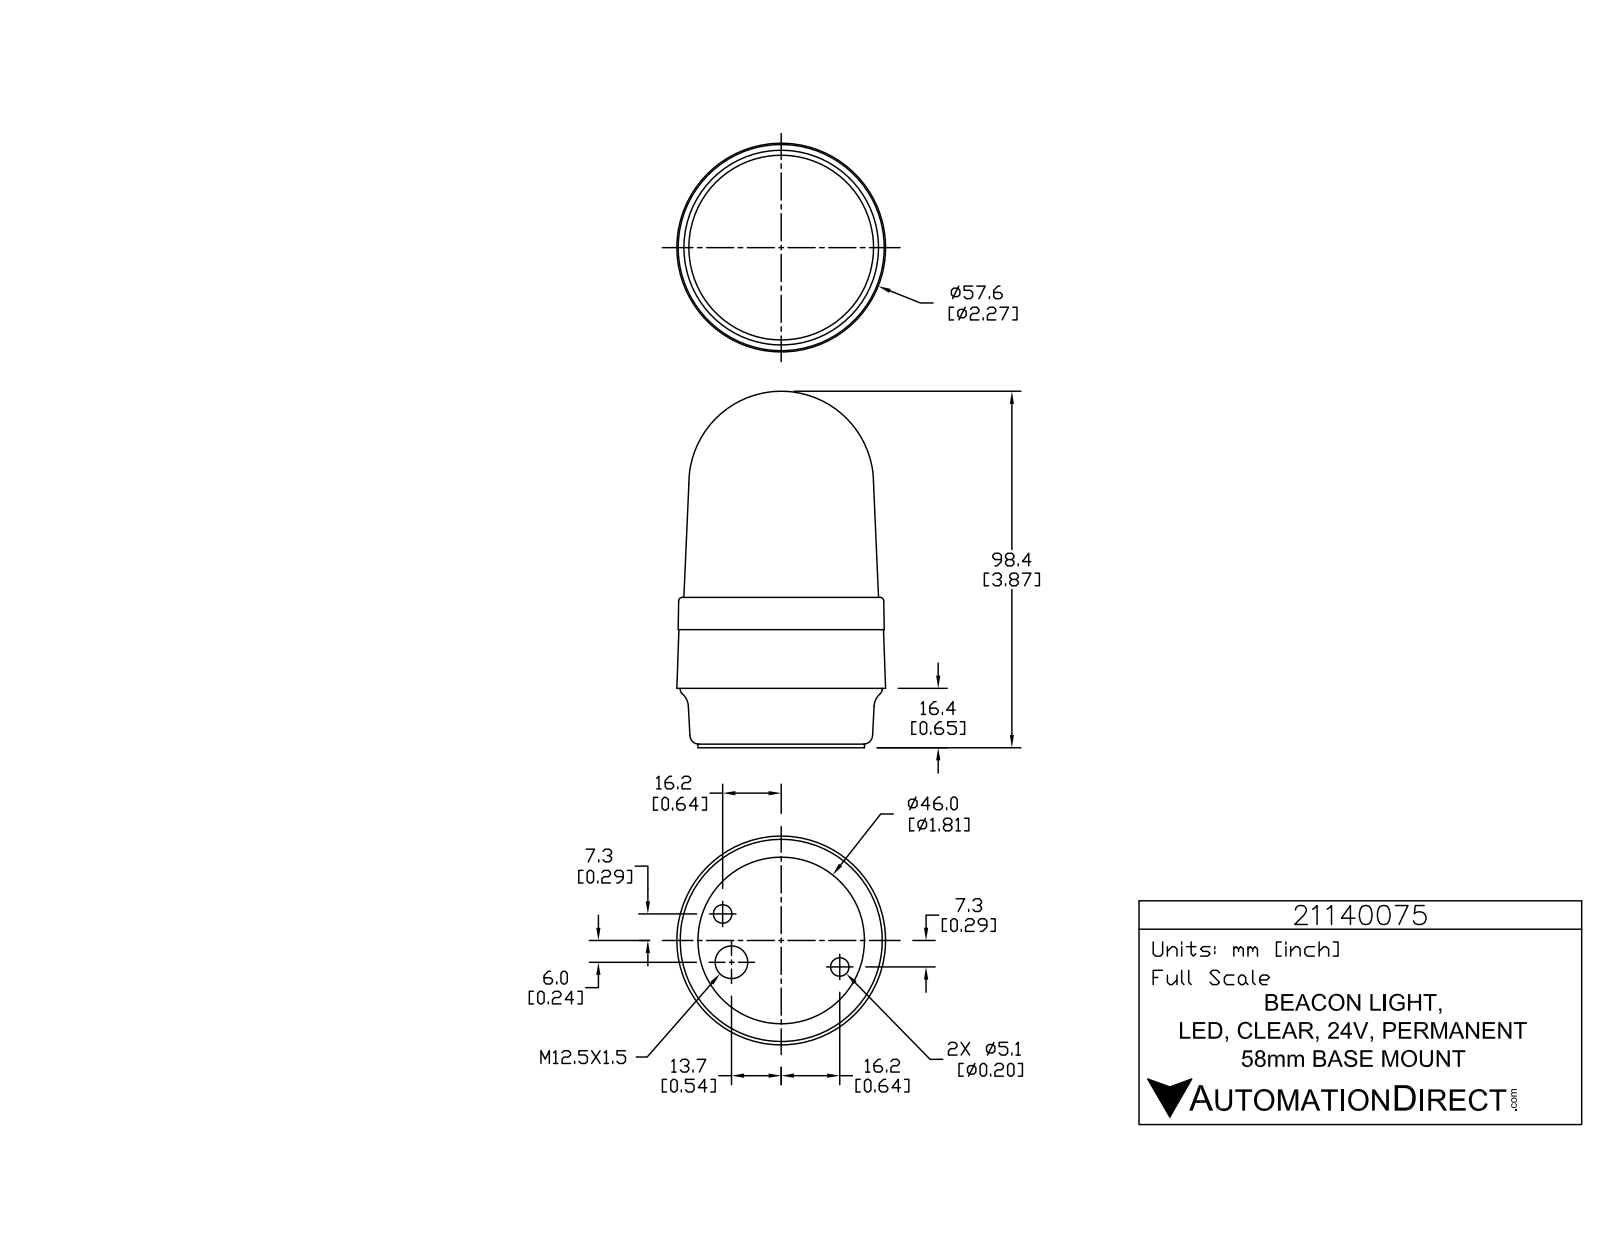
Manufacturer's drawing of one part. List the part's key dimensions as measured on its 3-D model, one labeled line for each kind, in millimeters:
Part name (STEP PRODUCT): 21140075
STEP written by: SolidWorks 2015 (AUTOMOTIVE_DESIGN)
Units: millimetres
Bodies: 1 solid, 764 faces (527 planar, 145 cylindrical, 92 other)
Overall size (bounding box): 98.4 × 57.63 × 57.63
Volume: 199 898 mm³ · Surface area: 18 922 mm²
Round holes (diameter × count): ⌀0.99 ×3, ⌀5.11 ×2, ⌀9 ×1
Round bosses / shafts (diameter × count): ⌀5.74 ×3, ⌀1.43 ×3, ⌀55.8 ×1, ⌀46 ×1
Partial cylindrical surfaces — rounded edges, fillets, slot ends (radius × count): R0.2 ×6, R0.21 ×6, R0.21 ×6, R3.32 ×6, R0.1 ×3, R0.12 ×3, R0.19 ×3, R0.2 ×3
Main face-to-face distances: 16.4, 1, 15.4, 41.5, 40.5, 25.1, 32.6, 31.6, 16.2, 8.9
Hole centre spacings: 13.56, 29.94, 35.5
